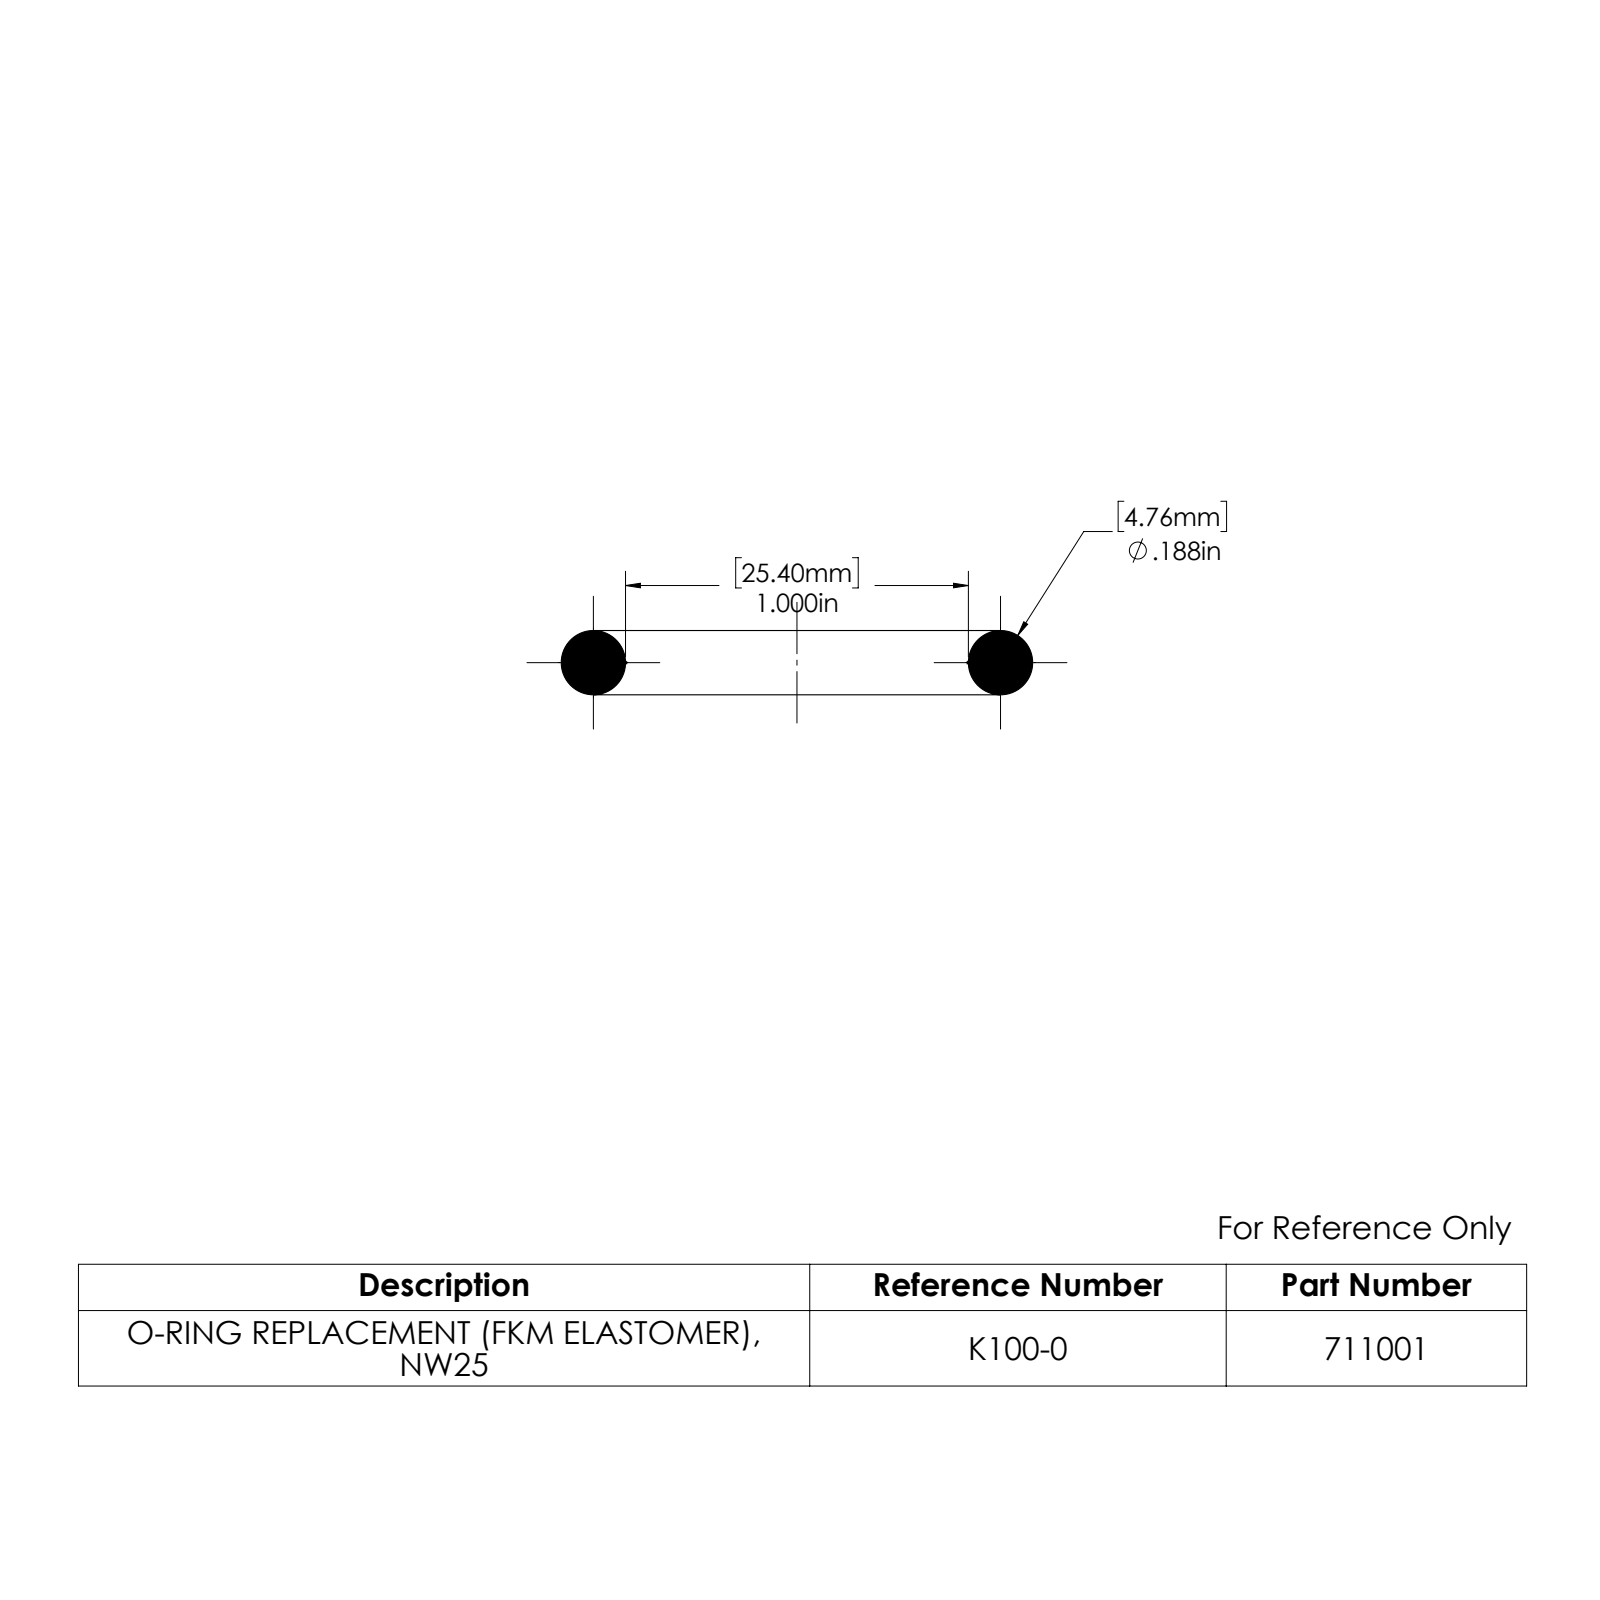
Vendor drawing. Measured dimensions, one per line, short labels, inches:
name: 711001
written by: SolidWorks 2022 (AUTOMOTIVE_DESIGN)
unit: in
bodies: 1 solid, 4 faces (0 planar, 0 cylindrical, 4 other)
size: 1.375 × 1.375 × 0.188
volume: 0.103 in³; area: 2.198 in²
